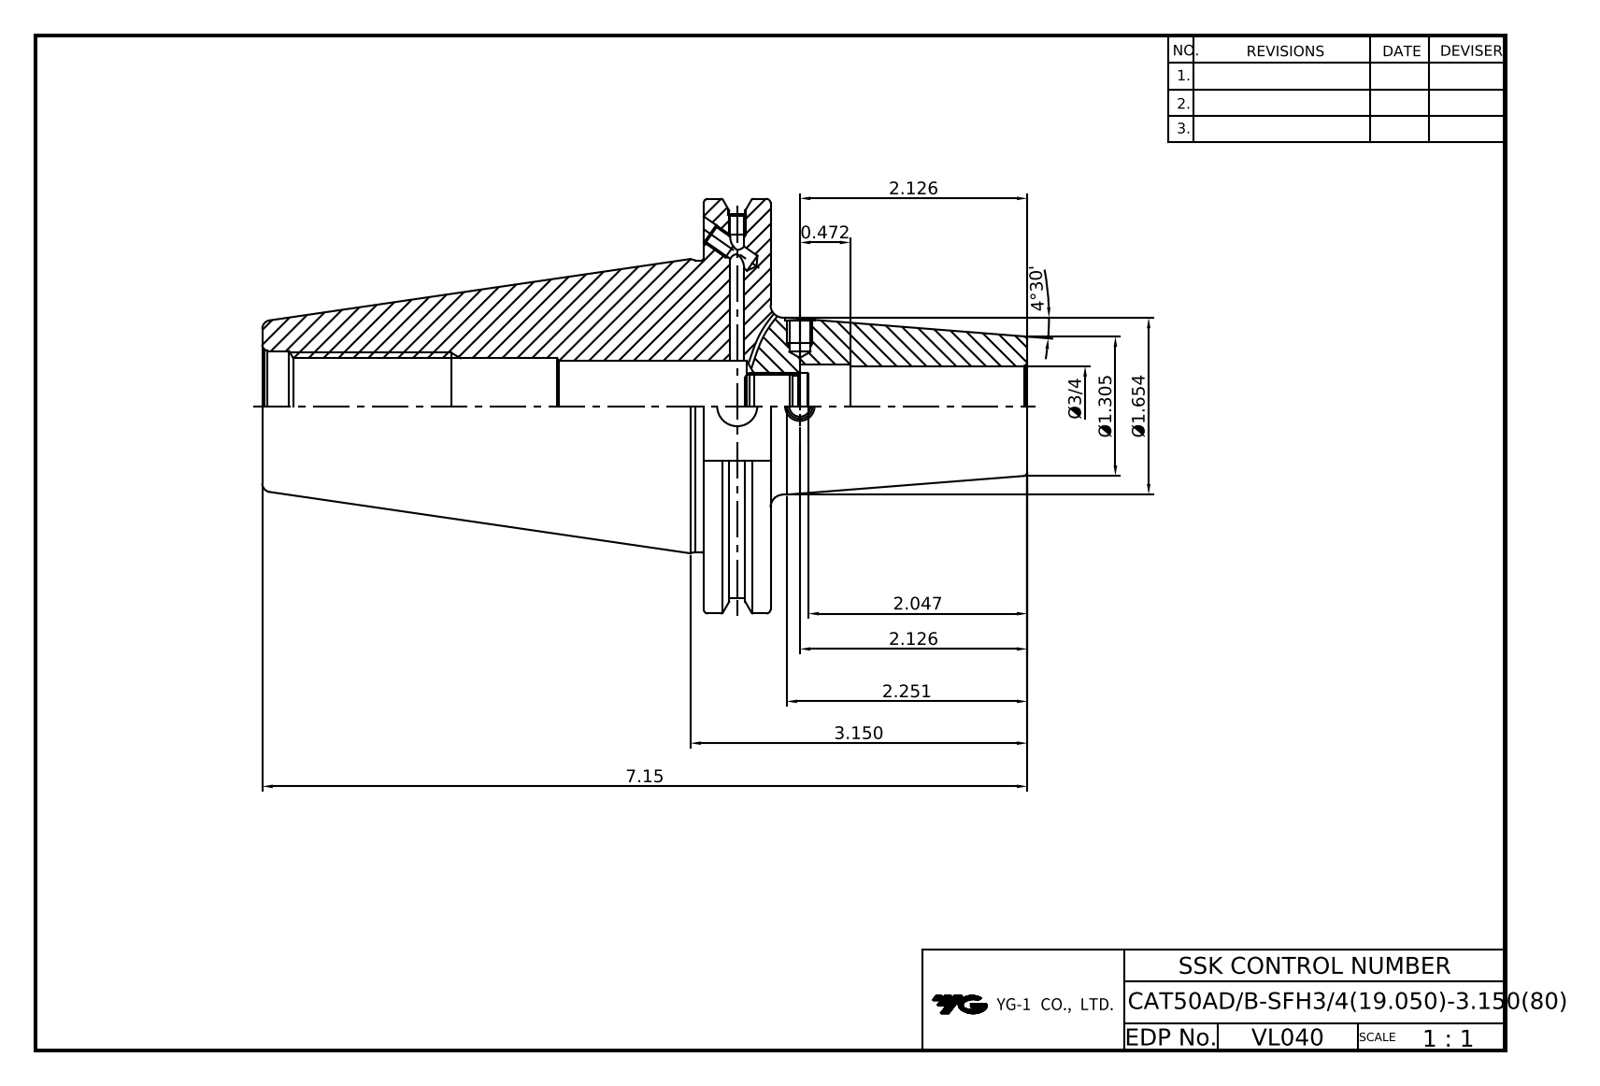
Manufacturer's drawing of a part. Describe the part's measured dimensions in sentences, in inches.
The part is named "LO-CAT50ADB-SFH19.05-80". Its 3-D file was written by "Autodesk Inventor 2025 (AUTOMOTIVE_DESIGN)". It is 1 solid with 84 faces: 37 planar, 26 cylindrical and 21 other. Overall it measures 7.15 by 3.875 by 3.728 inches. Its volume is 22.62 cubic inches and its surface area 85.35 square inches. Round holes: 2 of diameter 0.128, 2 of diameter 0.163, 2 of diameter 0.165, 2 of diameter 0.197, 1 of diameter 0.375, 1 of diameter 0.587, 1 of diameter 0.75, 1 of diameter 0.797, 1 of diameter 0.865, 1 of diameter 1.031. Round bosses or shafts: 1 of diameter 3.875, 1 of diameter 3.594, 1 of diameter 2.726, 1 of diameter 1.654. The main face-to-face distances are 0.625, 4.125, 4.75, 7.15, 3.025, 2.4, 2.875, 1.02, 4.363, 0.238.
